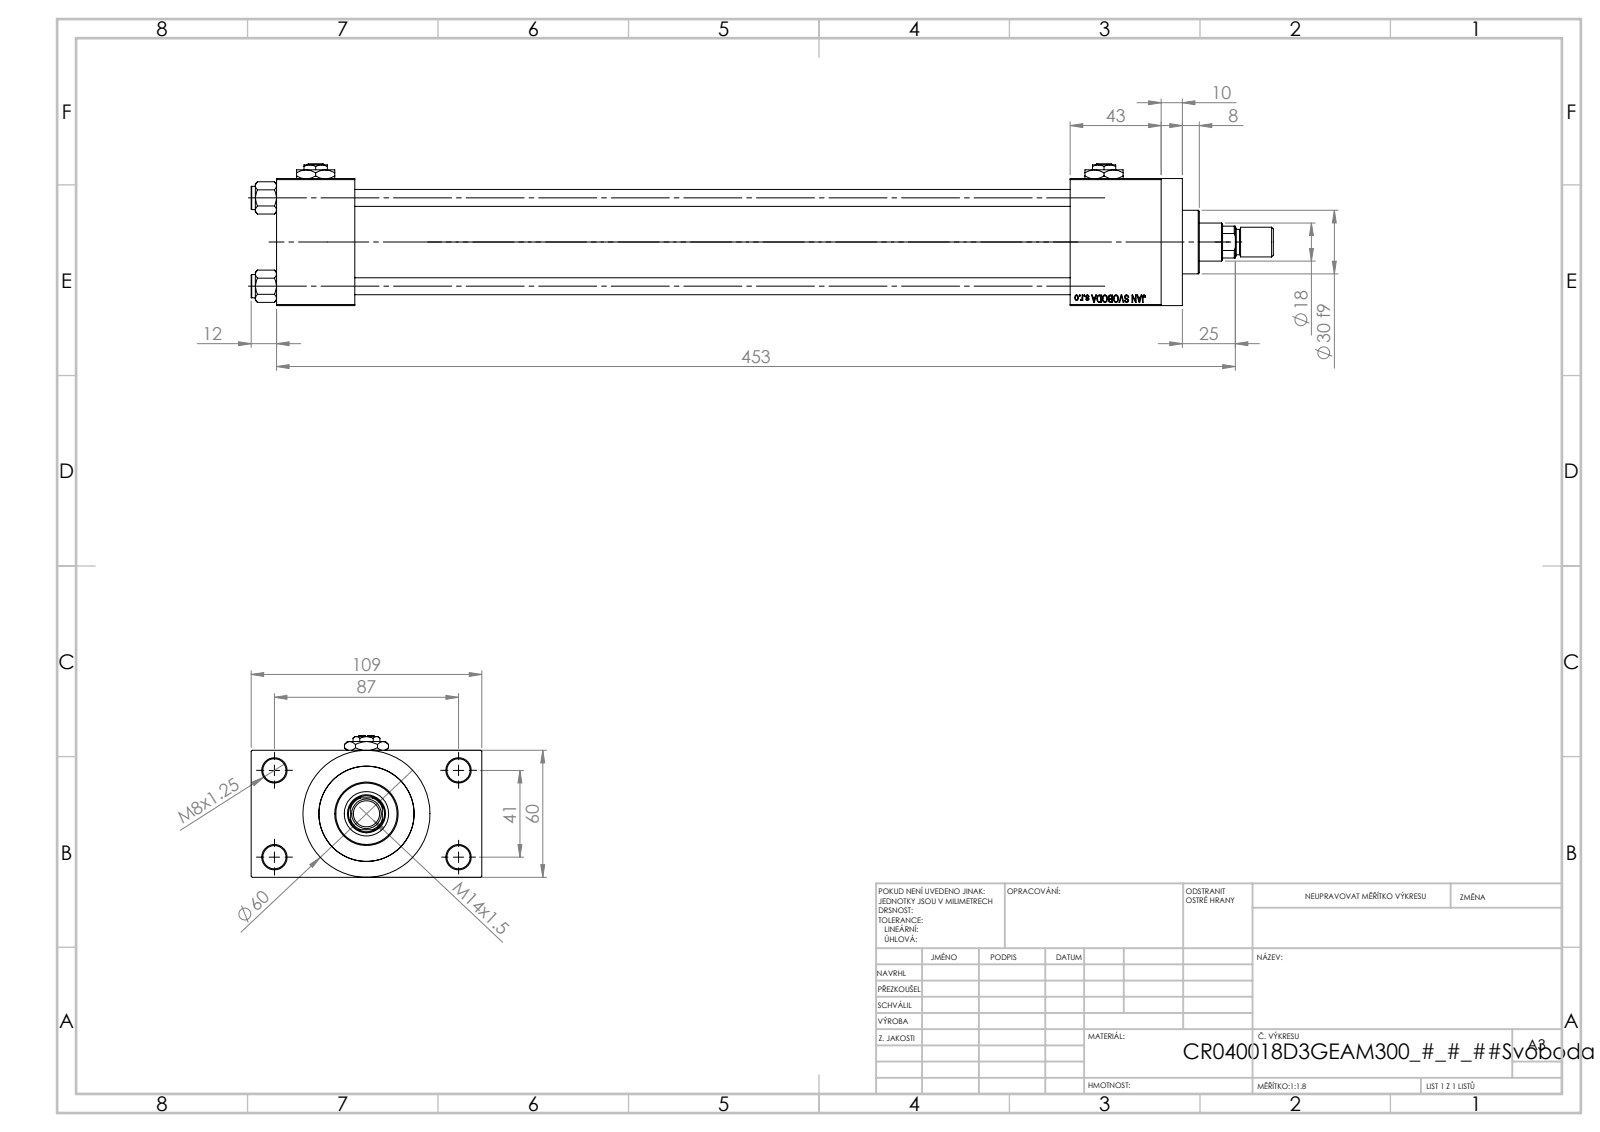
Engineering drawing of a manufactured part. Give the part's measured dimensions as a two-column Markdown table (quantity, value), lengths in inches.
| quantity | value |
| --- | --- |
| part name | ROD_END_AH; V215CR_D_TYCINKA; V215CR_D_Body; V215CR_VCP_D (+3 more) |
| STEP written by | SolidWorks 2019 (CONFIG_CONTROL_DESIGN) |
| units | inches |
| bodies | 14 solids, 1220 faces (550 planar, 104 cylindrical, 566 other) |
| overall size | 19.016 × 4.291 × 2.638 |
| volume | 46.33 in³ |
| surface area | 379.2 in² |
| round holes (diameter × count) | 0.315 × 4, 0.433 × 4, 0.276 × 2, 0.656 × 2, 0.945 × 2, 0.335 × 1, 0.709 × 1, 0.827 × 1, 1.22 × 1, 1.575 × 1, 1.772 × 1 |
| round bosses / shafts (diameter × count) | 0.433 × 4, 2.362 × 1, 1.811 × 1, 1.181 × 1, 0.551 × 1, 0.472 × 1 |
| partial cylindrical surfaces (radius × count) | 0.335 × 1 |
| main face-to-face distances | 2.362, 0.965, 3.327, 13.307, 1.457, 14.764, 1.693, 16.457, 15, 4.291 |
| hole center spacings | 0.892, 1.161, 1.642, 1.856, 1.893, 2.533, 3.011, 1.614 |
